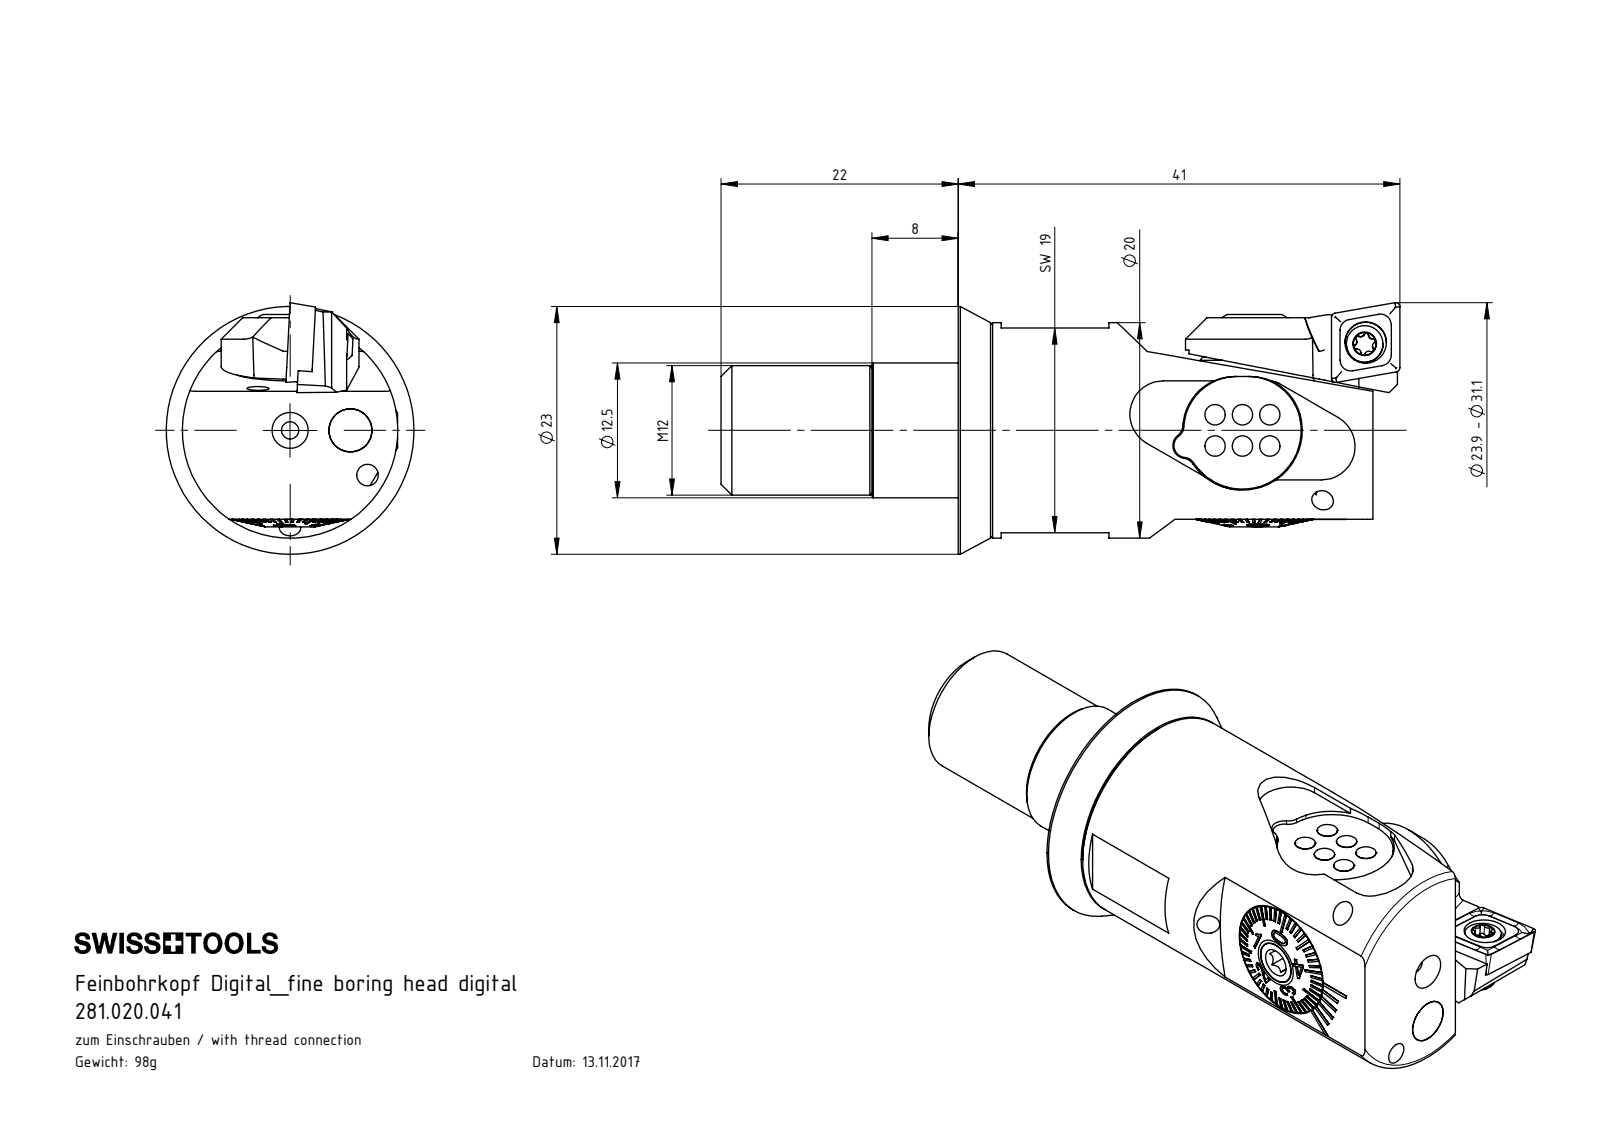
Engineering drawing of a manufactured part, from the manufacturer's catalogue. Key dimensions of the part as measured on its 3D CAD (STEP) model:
Part name (STEP PRODUCT): Klebstoff D4; HP4-ER2.008.028_A; HP4-F20.DA1.041_A; F20-WCA.001.005 (+8 more)
STEP written by: SolidWorks 2017 (CONFIG_CONTROL_DESIGN)
Units: millimetres
Bodies: 18 solids, 883 faces (387 planar, 193 cylindrical, 303 other)
Overall size (bounding box): 63 × 23.35 × 23
Volume: 12 613 mm³ · Surface area: 10 313 mm²
Round holes (diameter × count): ⌀2 ×5, ⌀3.3 ×3, ⌀0.7 ×1, ⌀1.6 ×1, ⌀1.9 ×1, ⌀2.05 ×1, ⌀2.4 ×1, ⌀2.5 ×1, ⌀2.8 ×1, ⌀3 ×1, ⌀3.85 ×1, ⌀4 ×1
Round bosses / shafts (diameter × count): ⌀1.9 ×6, ⌀6 ×2, ⌀4 ×2, ⌀3.95 ×2, ⌀23 ×1, ⌀20 ×1, ⌀12 ×1, ⌀10.98 ×1
Partial cylindrical surfaces — rounded edges, fillets, slot ends (radius × count): R0.21 ×6, R0.36 ×5, R1.1 ×3, R1.2 ×3, R5 ×3, R0.3 ×2, R0.5 ×2, R2 ×2
Main face-to-face distances: 3, 38.5, 35.5, 15.05, 8, 1.5, 11, 46.5, 6, 2.8
Hole centre spacings: 1.14, 2.6, 3.51, 4.44, 5.6, 8.3
